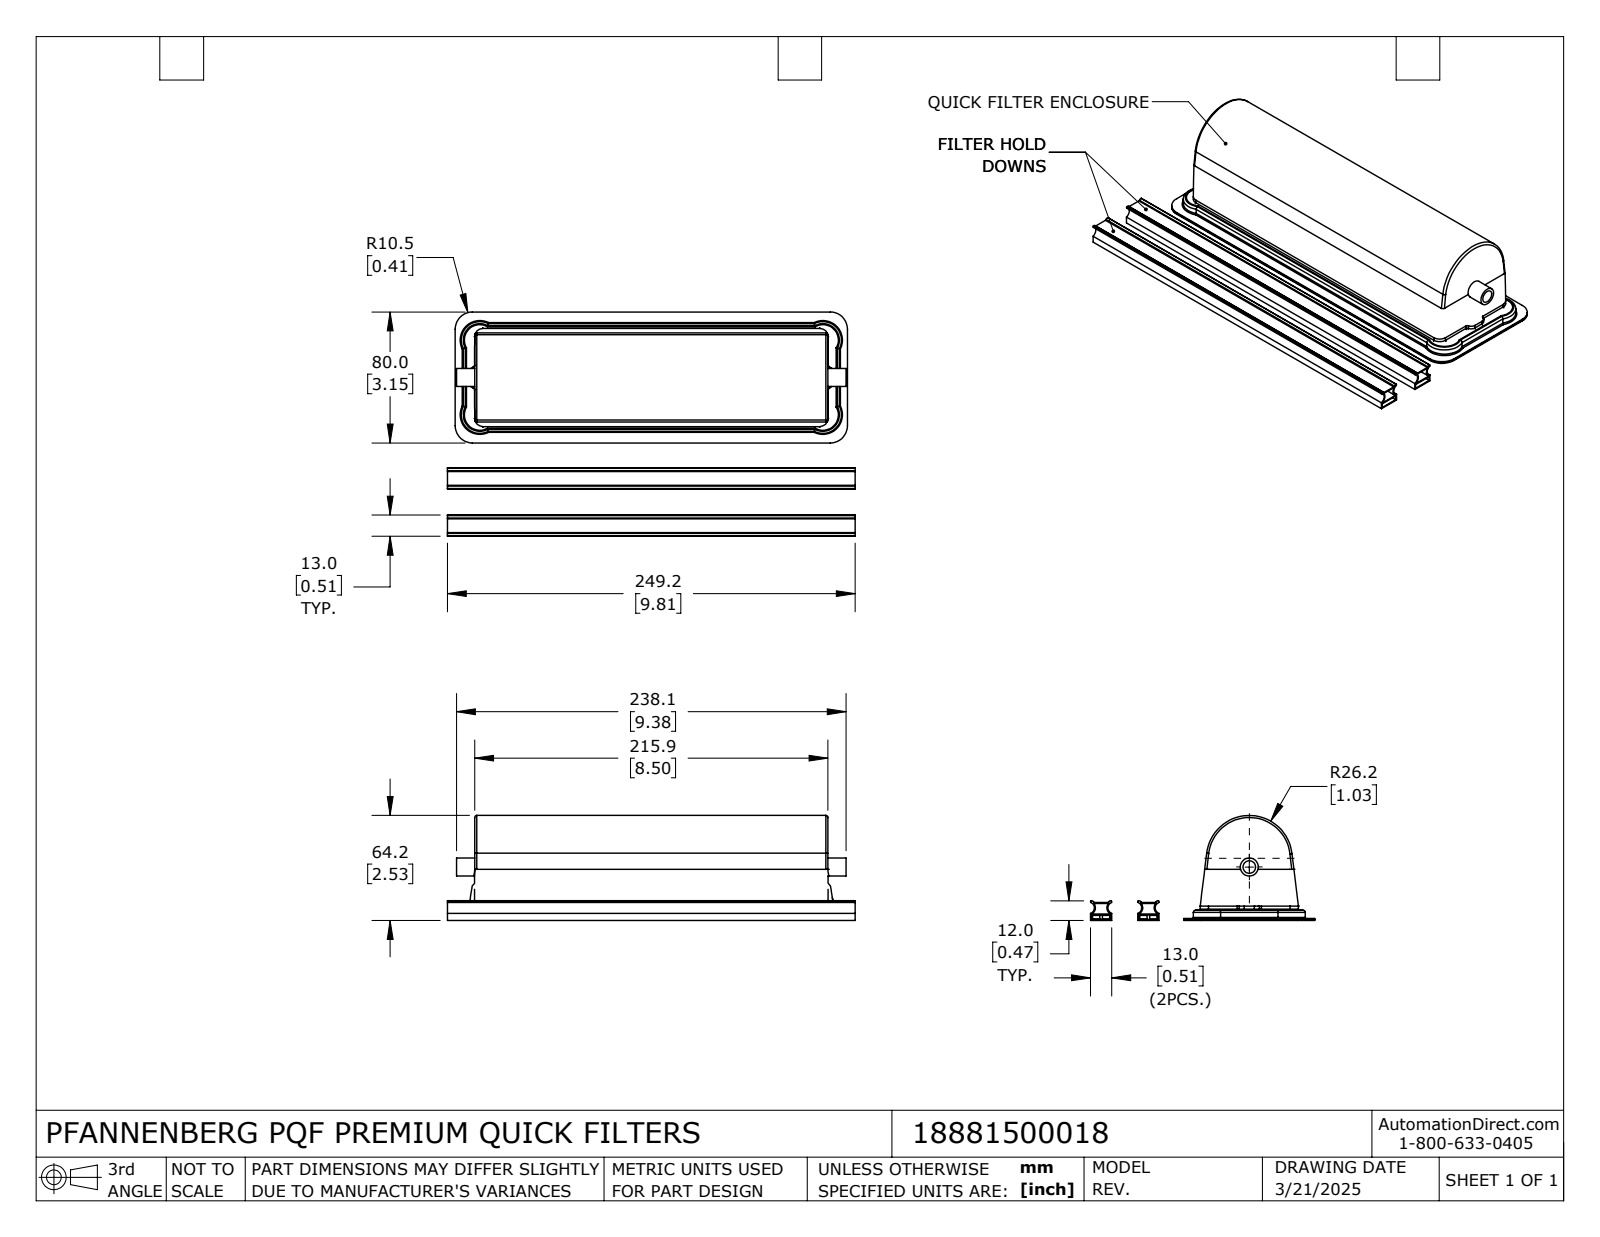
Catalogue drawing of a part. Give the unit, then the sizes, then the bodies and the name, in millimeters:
Units: millimetres
Overall size (bounding box): 249.2 × 137 × 64.2
Round holes (diameter × count): ⌀10.5 ×2, ⌀7.7 ×1, ⌀11 ×1
Round bosses / shafts (diameter × count): ⌀1.6 ×8, ⌀10.5 ×4, ⌀11.8 ×2, ⌀50.8 ×1
Partial cylindrical surfaces — rounded edges, fillets, slot ends (radius × count): R0.6 ×42, R1.3 ×42, R5 ×8, R0.5 ×4, R0.7 ×4, R1.1 ×4, R1.2 ×4, R1.9 ×4
Main face-to-face distances: 0.6, 3.4, 2.7, 10.4, 7.1, 5.7, 2.3, 4.7, 9.8, 5
Hole centre spacings: 135.2
Volume: 486 400 mm³ · Surface area: 261 800 mm²
Bodies: 12 solids, 426 faces (116 planar, 196 cylindrical, 114 other)
Part name (STEP PRODUCT): PQF-XXX_MAG-STRIP; PQF-XXX; PQF-XXX_1; PQF-XXX_ROLL (+1 more)
STEP written by: SolidWorks 2024 (AUTOMOTIVE_DESIGN)
